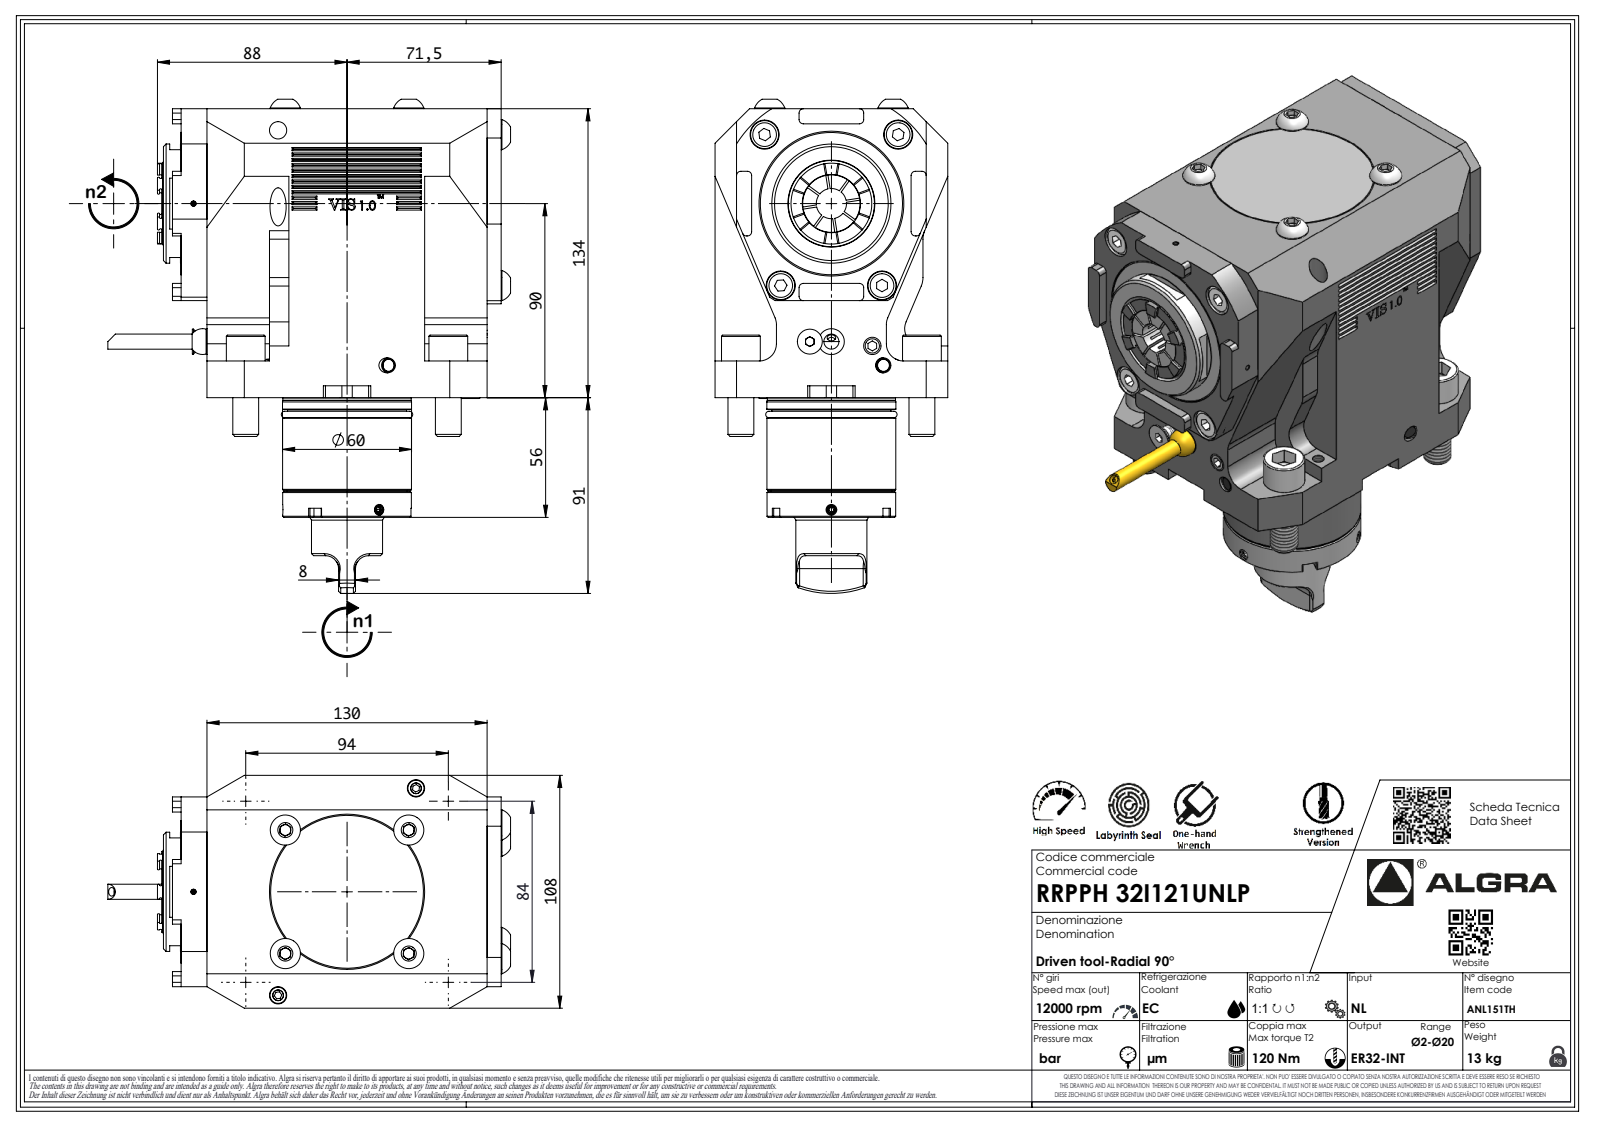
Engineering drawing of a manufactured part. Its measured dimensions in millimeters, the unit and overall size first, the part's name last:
Units: millimetres
Overall size (bounding box): 224.8 × 182.5 × 108
Round holes (diameter × count): ⌀2.1 ×1
Round bosses / shafts (diameter × count): ⌀18 ×4, ⌀12 ×4, ⌀59.9 ×1, ⌀59.8 ×1, ⌀59.7 ×1, ⌀59.5 ×1, ⌀55.2 ×1, ⌀55 ×1
Partial cylindrical surfaces — rounded edges, fillets, slot ends (radius × count): R8 ×22, R2 ×16, R0.33 ×7, R0.52 ×7, R3.7 ×7, R6 ×6, R10 ×4, R3 ×3
Main face-to-face distances: 108, 134, 12, 29, 101, 148.5, 136.5, 49, 72, 5.5
Volume: 1 985 000 mm³ · Surface area: 123 136 mm²
Bodies: 1 solid, 631 faces (388 planar, 115 cylindrical, 128 other)
Part name (STEP PRODUCT): RRPPH32I121UNLP
STEP written by: SolidWorks 2023 (AUTOMOTIVE_DESIGN)
